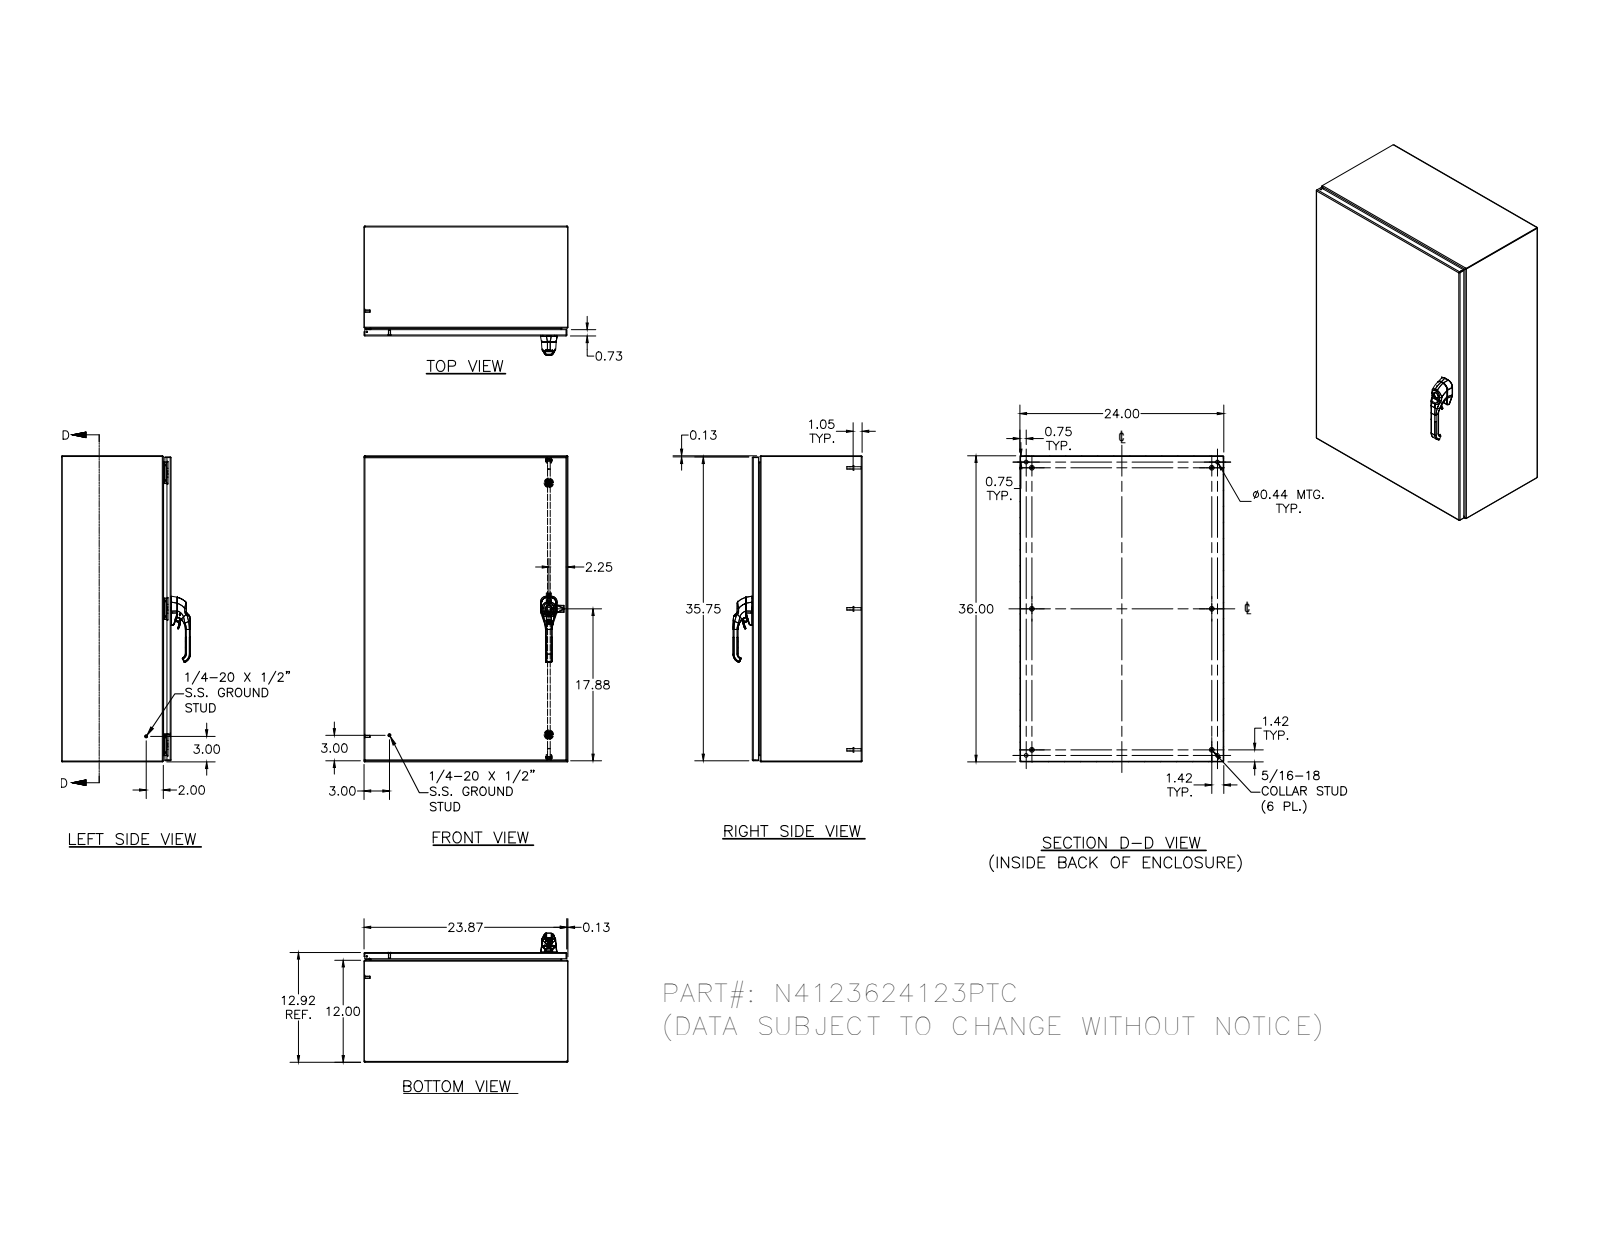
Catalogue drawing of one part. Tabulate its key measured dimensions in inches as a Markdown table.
| quantity | value |
| --- | --- |
| part name | N4123624123PTC; N4123624123PTCBKP; N41236243PTCLID; HFW328176 (+8 more) |
| STEP written by | Autodesk Inventor 2011 (AUTOMOTIVE_DESIGN) |
| units | inches |
| bodies | 60 solids, 3398 faces (1066 planar, 1279 cylindrical, 1053 other) |
| overall size | 36 × 24 × 15.186 |
| volume | 256.4 in³ |
| surface area | 7 007 in² |
| round holes (diameter × count) | 0.188 × 7, 0.093 × 6, 0.152 × 6, 0.167 × 6, 0.172 × 6, 0.165 × 4, 0.197 × 4, 0.437 × 4, 0.156 × 3, 0.213 × 3, 0.236 × 3, 0.354 × 3 |
| round bosses / shafts (diameter × count) | 0.25 × 14, 0.563 × 6, 0.36 × 6, 0.32 × 6, 0.3 × 6, 0.275 × 6, 0.256 × 6, 0.164 × 6 |
| partial cylindrical surfaces (radius × count) | 0.02 × 179, 0.012 × 79, 0.05 × 38, 0.031 × 34, 0.118 × 33, 0.016 × 26, 0.125 × 21, 0.105 × 20 |
| main face-to-face distances | 0.074, 12.843, 23.926, 12.769, 12.917, 35.926, 23.852, 24, 36, 35.852 |
| hole center spacings | 16, 15.996, 16.008, 31.996, 0.017, 0.66, 16.004, 16.656 |
